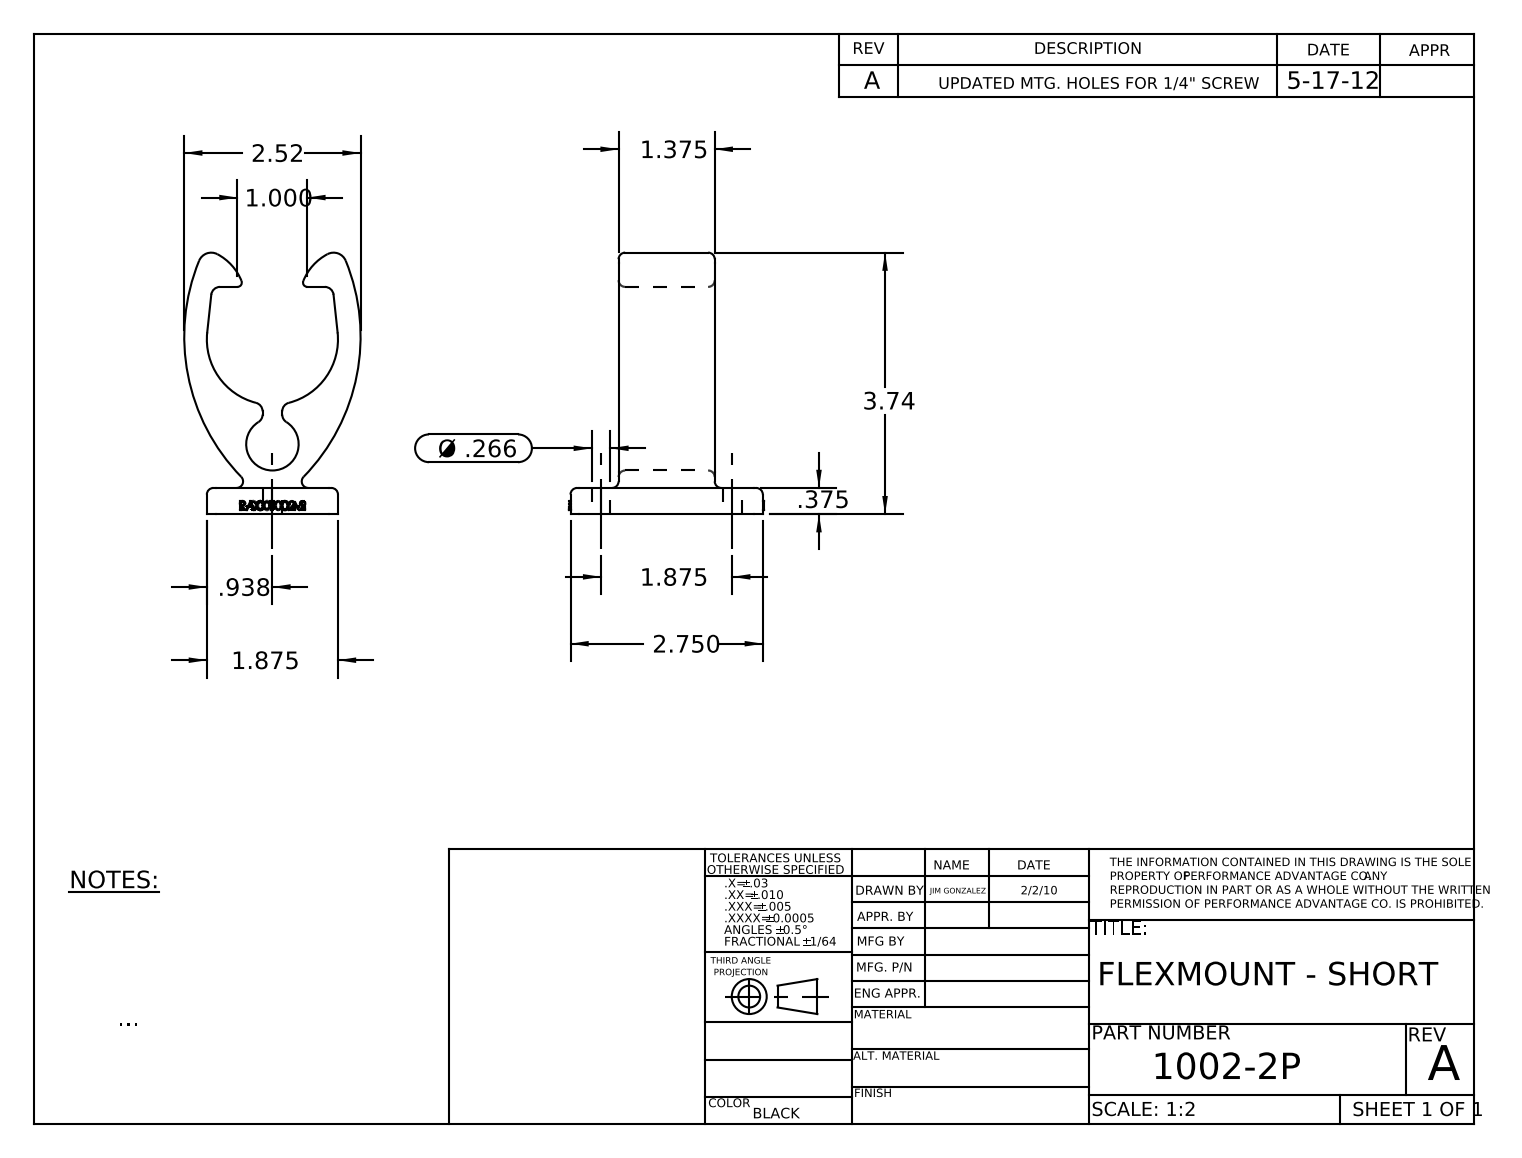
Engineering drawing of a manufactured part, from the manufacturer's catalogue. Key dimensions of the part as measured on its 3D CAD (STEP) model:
Part name (STEP PRODUCT): 1002-2P
STEP written by: SolidWorks 2014 (CONFIG_CONTROL_DESIGN)
Units: inches
Bodies: 1 solid, 325 faces (126 planar, 51 cylindrical, 148 other)
Overall size (bounding box): 3.74 × 2.781 × 2.521
Volume: 6.223 in³ · Surface area: 39.85 in²
Round holes (diameter × count): ⌀0.266 ×2, ⌀0.75 ×1
Partial cylindrical surfaces — rounded edges, fillets, slot ends (radius × count): R0.094 ×18, R0.125 ×10, R0.062 ×2, R0.188 ×2, R0.75 ×2, R2.875 ×2, R0.938 ×1
Main face-to-face distances: 0.375, 1.375, 0.687, 2.062, 1.875, 3.25, 2.875, 2.75, 0.797, 1.078
Hole centre spacings: 1.875
